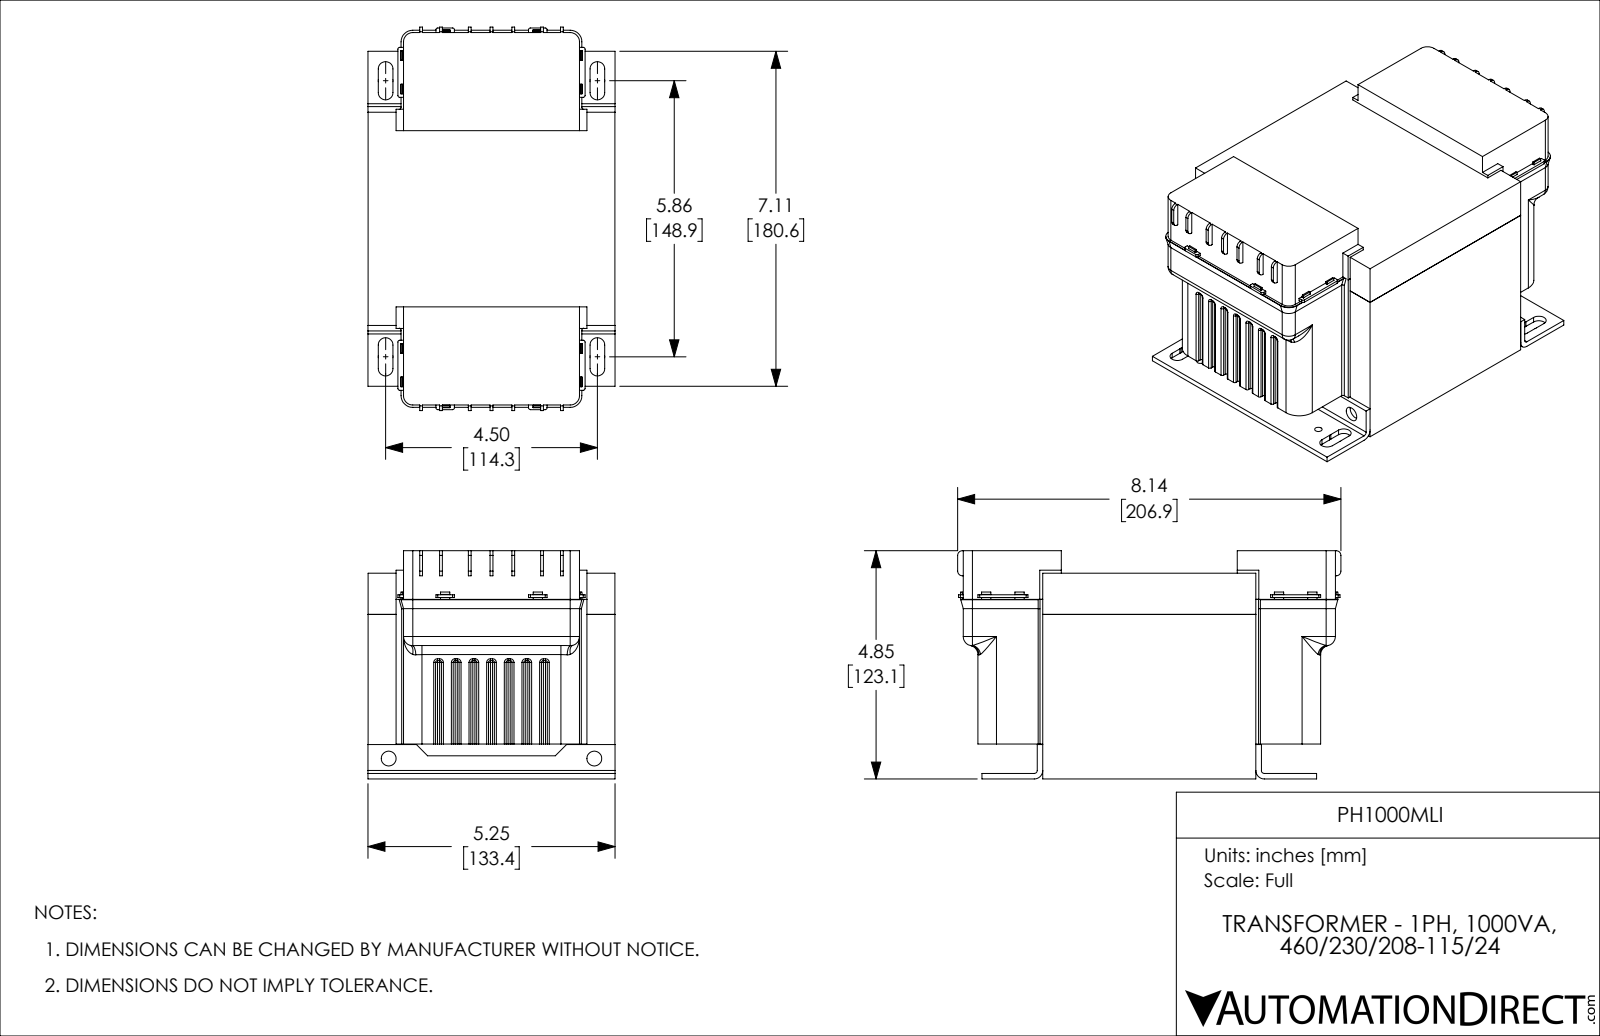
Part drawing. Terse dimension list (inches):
name: PH1000MLI
written by: SolidWorks 2021 (CONFIG_CONTROL_DESIGN)
unit: in
bodies: 8 solids, 718 faces (410 planar, 218 cylindrical, 90 other)
size: 8.145 × 5.25 × 4.847
volume: 153.7 in³; area: 373.6 in²
holes: 4× ⌀0.157, 2× ⌀0.315
rounds: 94× R0.039, 10× R0.197, 8× R0.156, 4× R0.1, 4× R0.157, 4× R0.248, 4× R0.394, 2× R0.063
face distances: 4.528, 3.496, 4.37, 0.874, 3.814, 0.318, 0.556, 5.244, 0.752, 4.492
hole spacings: 3.543, 5.931, 6.909, 4.37
